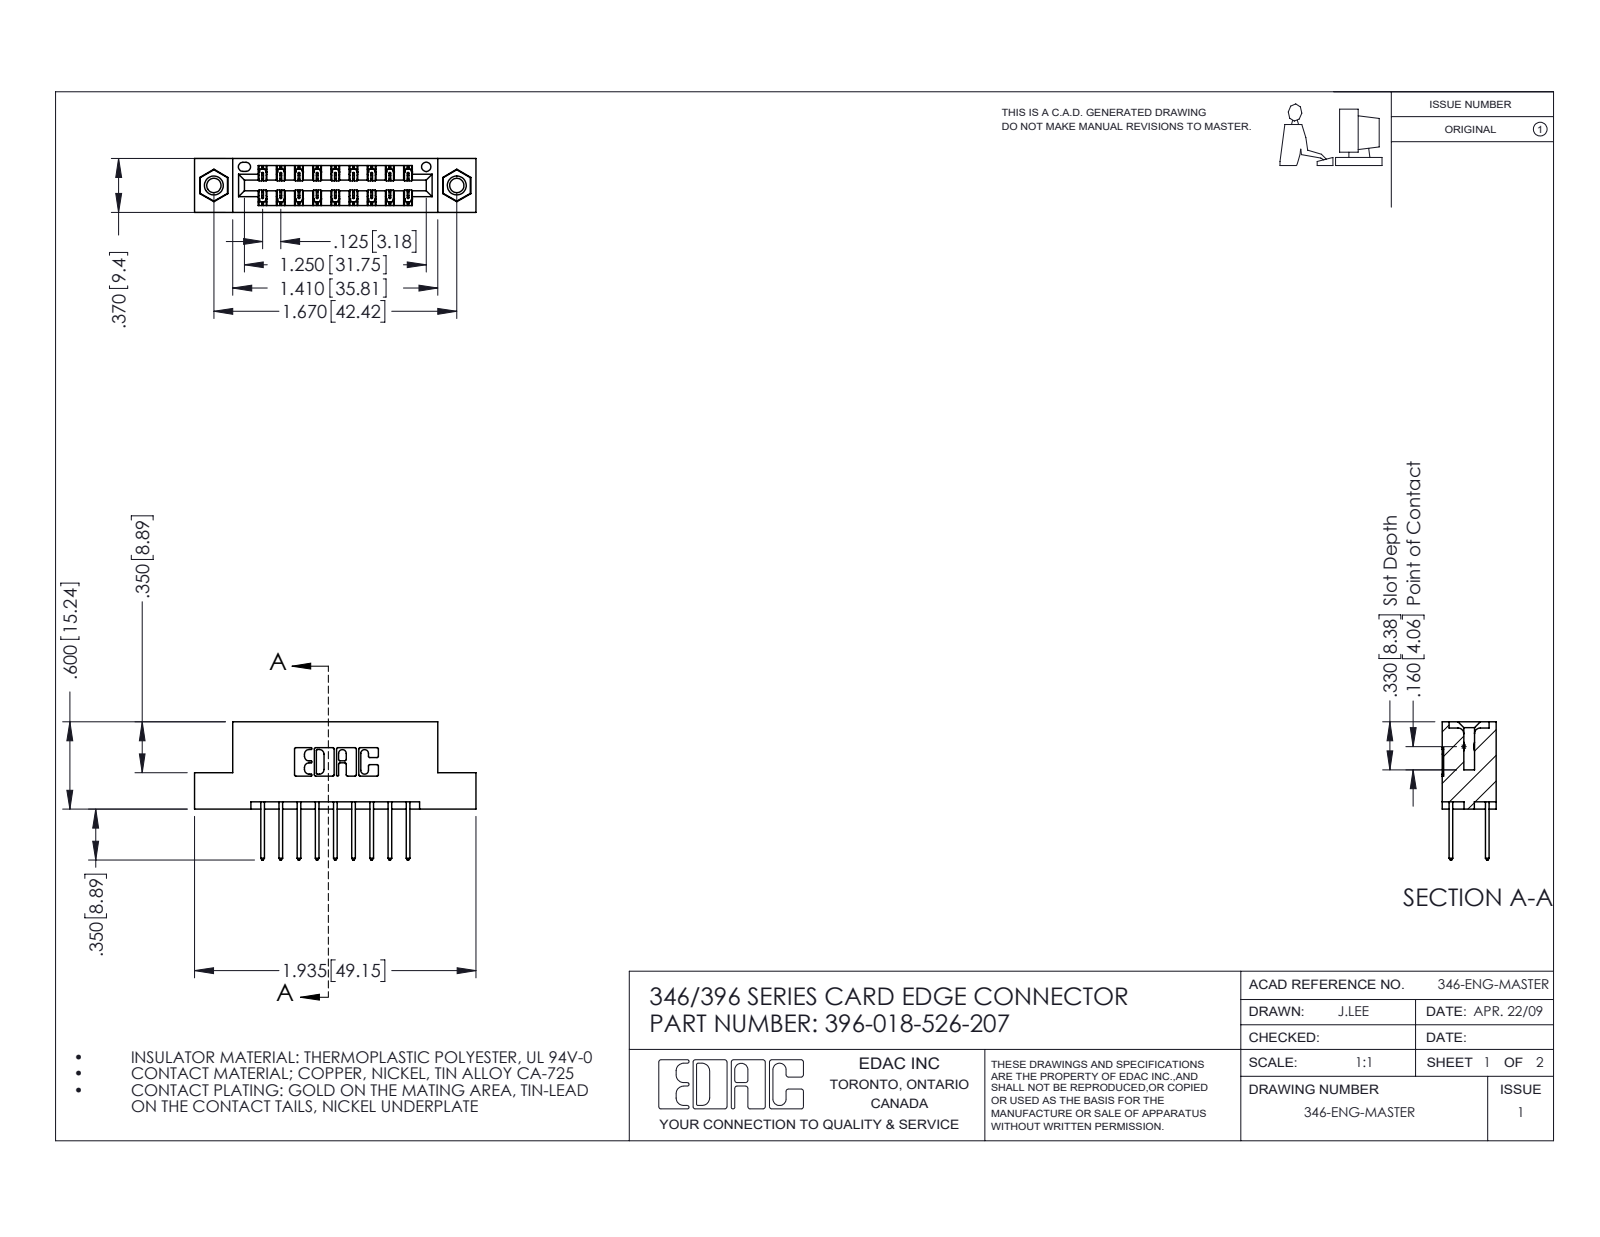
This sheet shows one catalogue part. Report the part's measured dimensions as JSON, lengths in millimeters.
{"part_name": "345-250-001_345-250-005-103; 345-292-001_345-293-126; 346 Part_Flush Mounting Lugs - 0.156 Dia-TI; 396-018-526-207", "step_written_by": "SolidWorks 2016 (CONFIG_CONTROL_DESIGN)", "units": "millimeters", "bodies": {"solids": 21, "faces": 1118, "planar": 738, "cylindrical": 364, "other": 16}, "overall_size": [49.1, 24.1, 9.4], "volume_mm3": 4560, "surface_area_mm2": 5905, "round_holes": [[2.5, 2], [3.2, 2], [4, 2], [1.6, 1]], "round_bosses_or_shafts": [[3.9, 2]], "partial_cylinders_radius": [[0.2, 27], [0.3, 22], [0.3, 18], [0.2, 6], [0.8, 6], [0.7, 3], [0.4, 2], [0.6, 2]], "face_to_face_distances": [6.4, 1.2, 8.2, 9.4, 1.8, 7.6, 0.6, 7, 3.8, 5.6], "hole_center_spacings": [6.2, 37.2, 42.4]}
